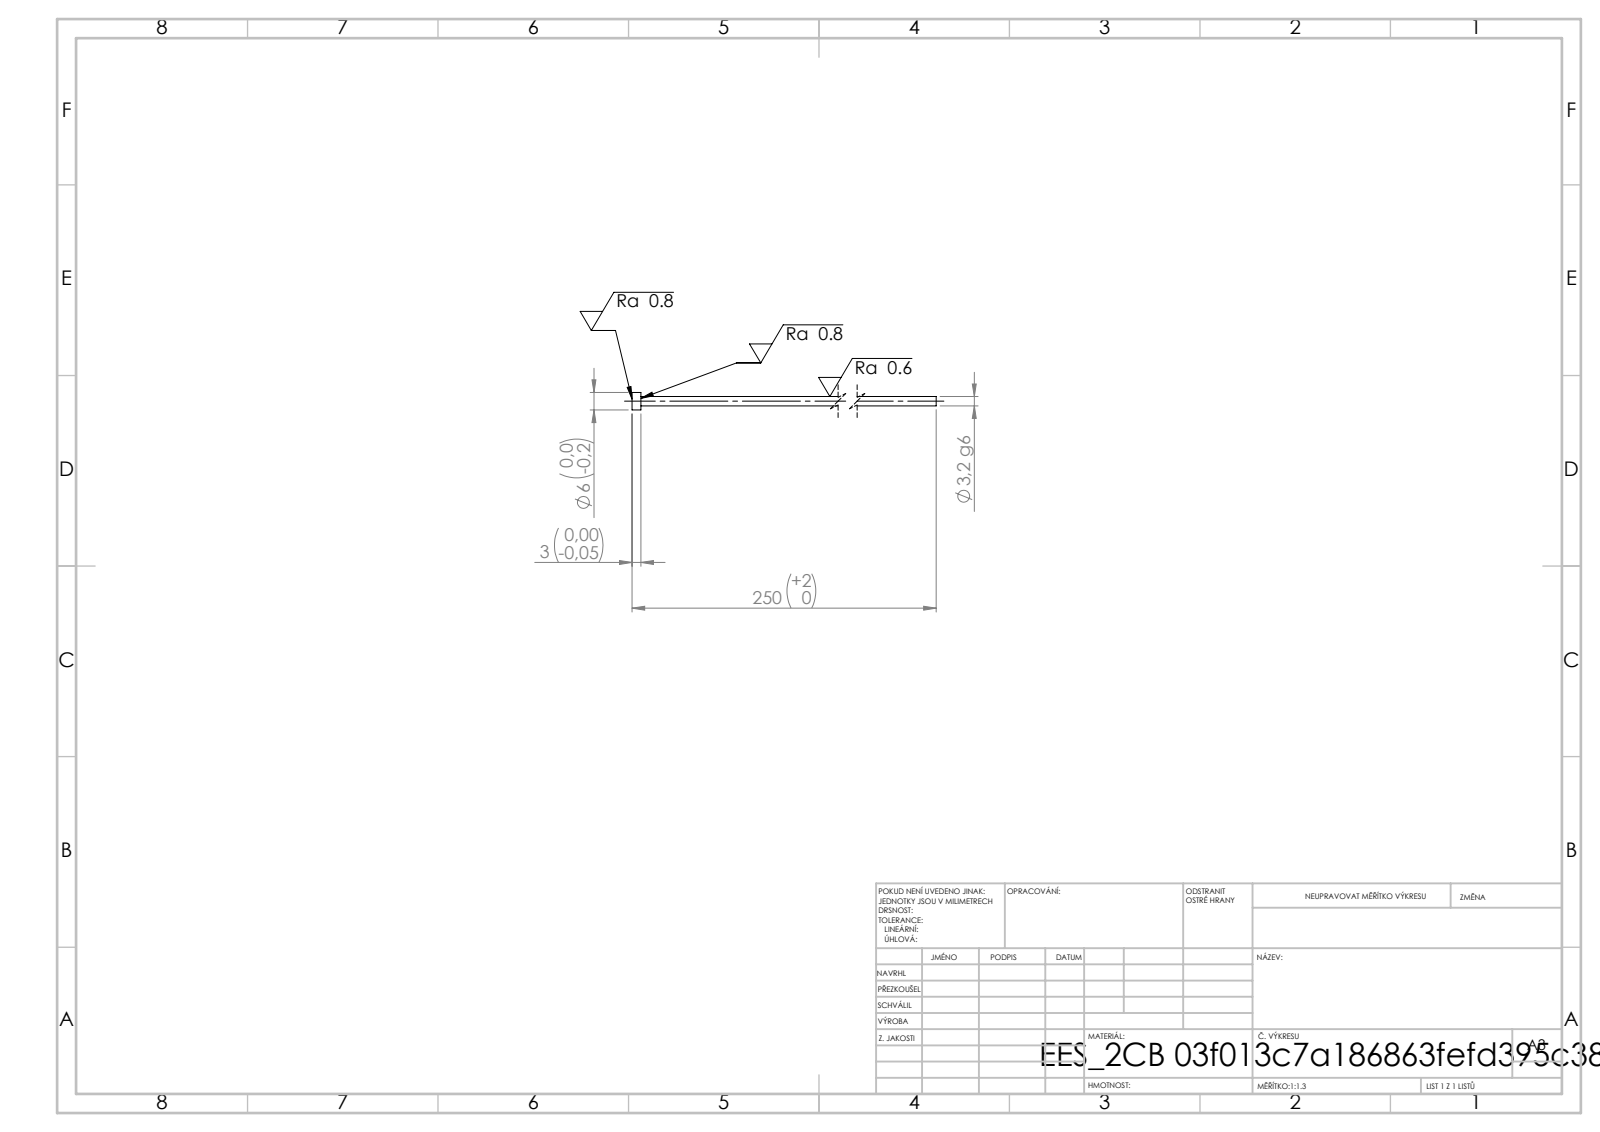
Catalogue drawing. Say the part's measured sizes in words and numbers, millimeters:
Its 3-D file was written by "SolidWorks 2019 (CONFIG_CONTROL_DESIGN)". It is 1 solid with 7 faces: 3 planar, 4 cylindrical and 0 other. Overall it measures 250 by 6 by 6 millimeters. Its volume is 2 071 cubic millimeters and its surface area 2 596 square millimeters. Round bosses or shafts: 1 of diameter 6, 1 of diameter 3.2. The main face-to-face distances are 3, 250, 247.
